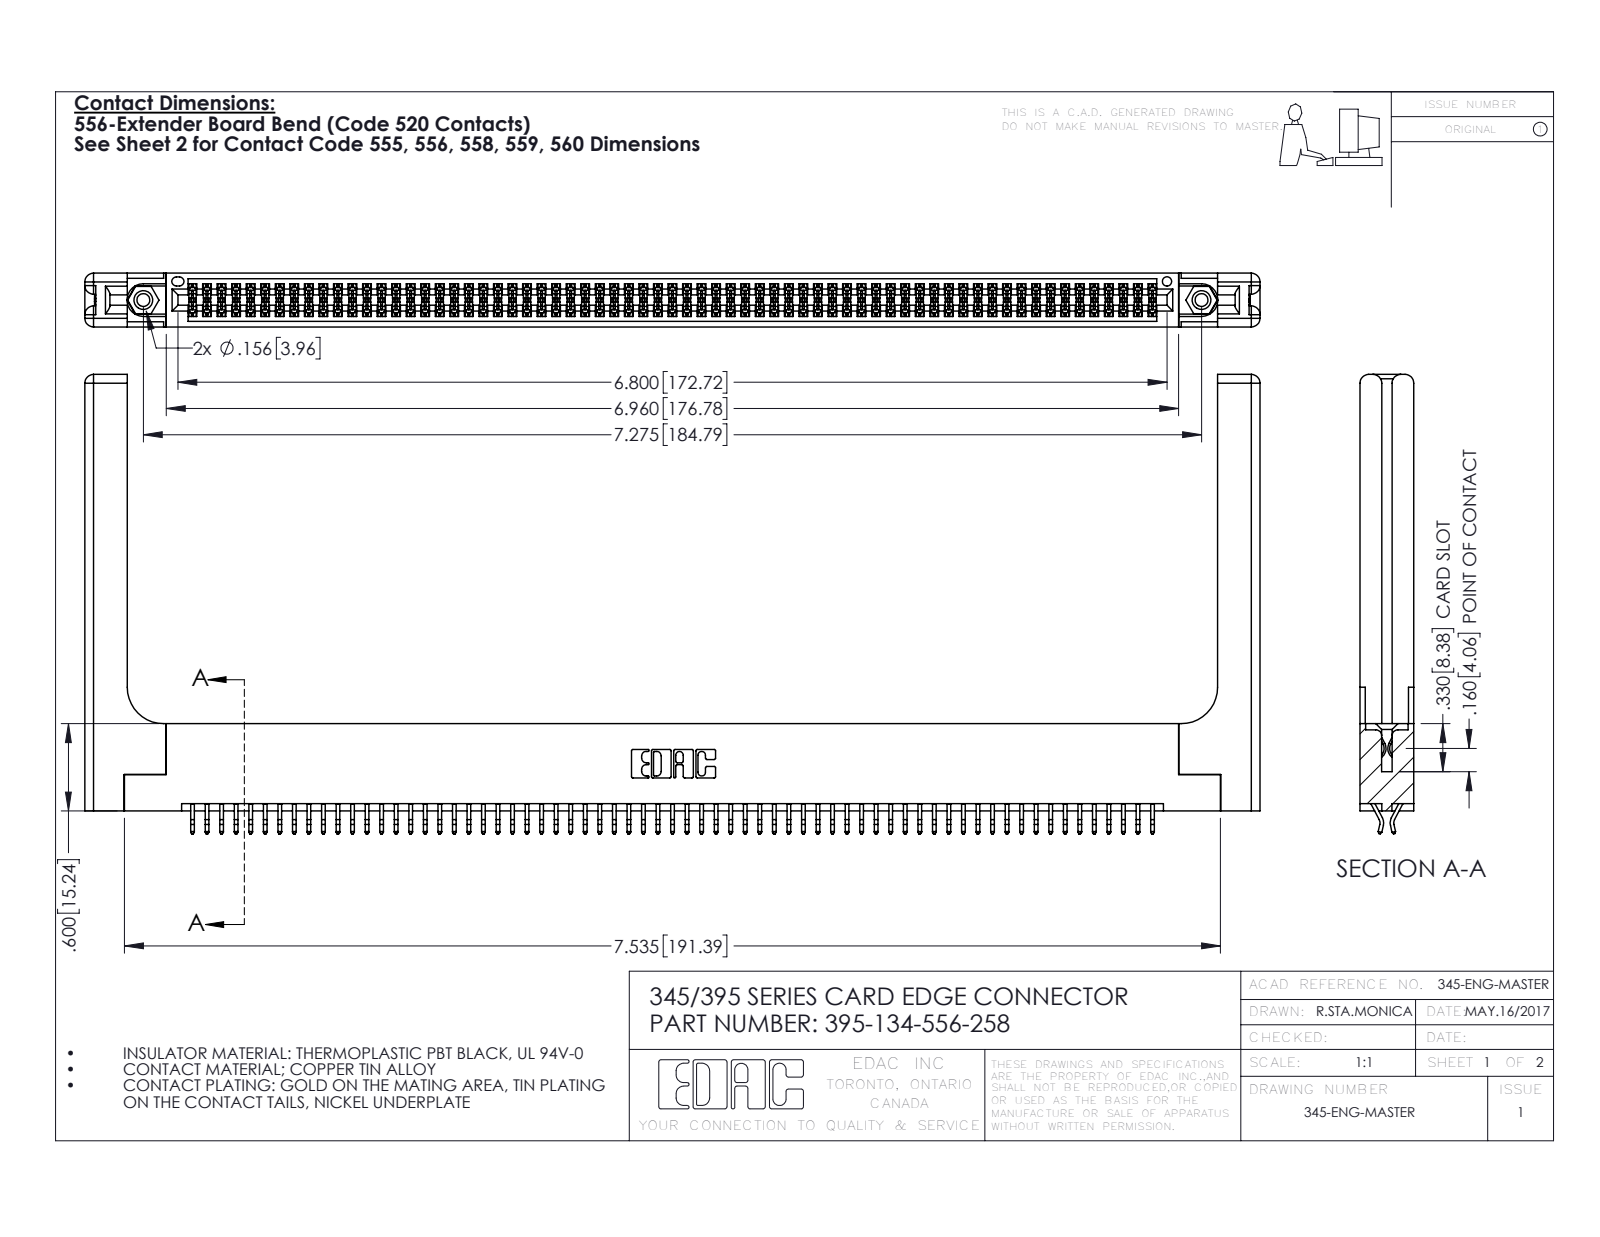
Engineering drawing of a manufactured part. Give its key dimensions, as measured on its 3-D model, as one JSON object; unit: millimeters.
{"part_name": "345-292-001_556 Tail; 345-220-058_345-220-058; 345-250-001_345-250-001-102; 345 Part_Flush Mounting Lugs - 0.156 Dia-TH (+1 more)", "step_written_by": "SolidWorks 2016 (CONFIG_CONTROL_DESIGN)", "units": "millimeters", "bodies": {"solids": 139, "faces": 7886, "planar": 5186, "cylindrical": 2640, "other": 60}, "overall_size": [205.2, 80.2, 9.4], "volume_mm3": 28630, "surface_area_mm2": 35230, "round_holes": [[2.3, 2], [3.2, 2], [4, 2], [1.6, 1]], "round_bosses_or_shafts": [[3.9, 2]], "partial_cylinders_radius": [[0.2, 201], [0.3, 22], [1.5, 16], [0.2, 6], [0.8, 6], [0.7, 3], [0.3, 2], [0.4, 2]], "face_to_face_distances": [1.8, 7.6, 9.4, 5.1, 0.6, 2.5, 6.9, 5.7, 3.8, 3.8], "hole_center_spacings": [6.9, 178.8, 184.8]}
